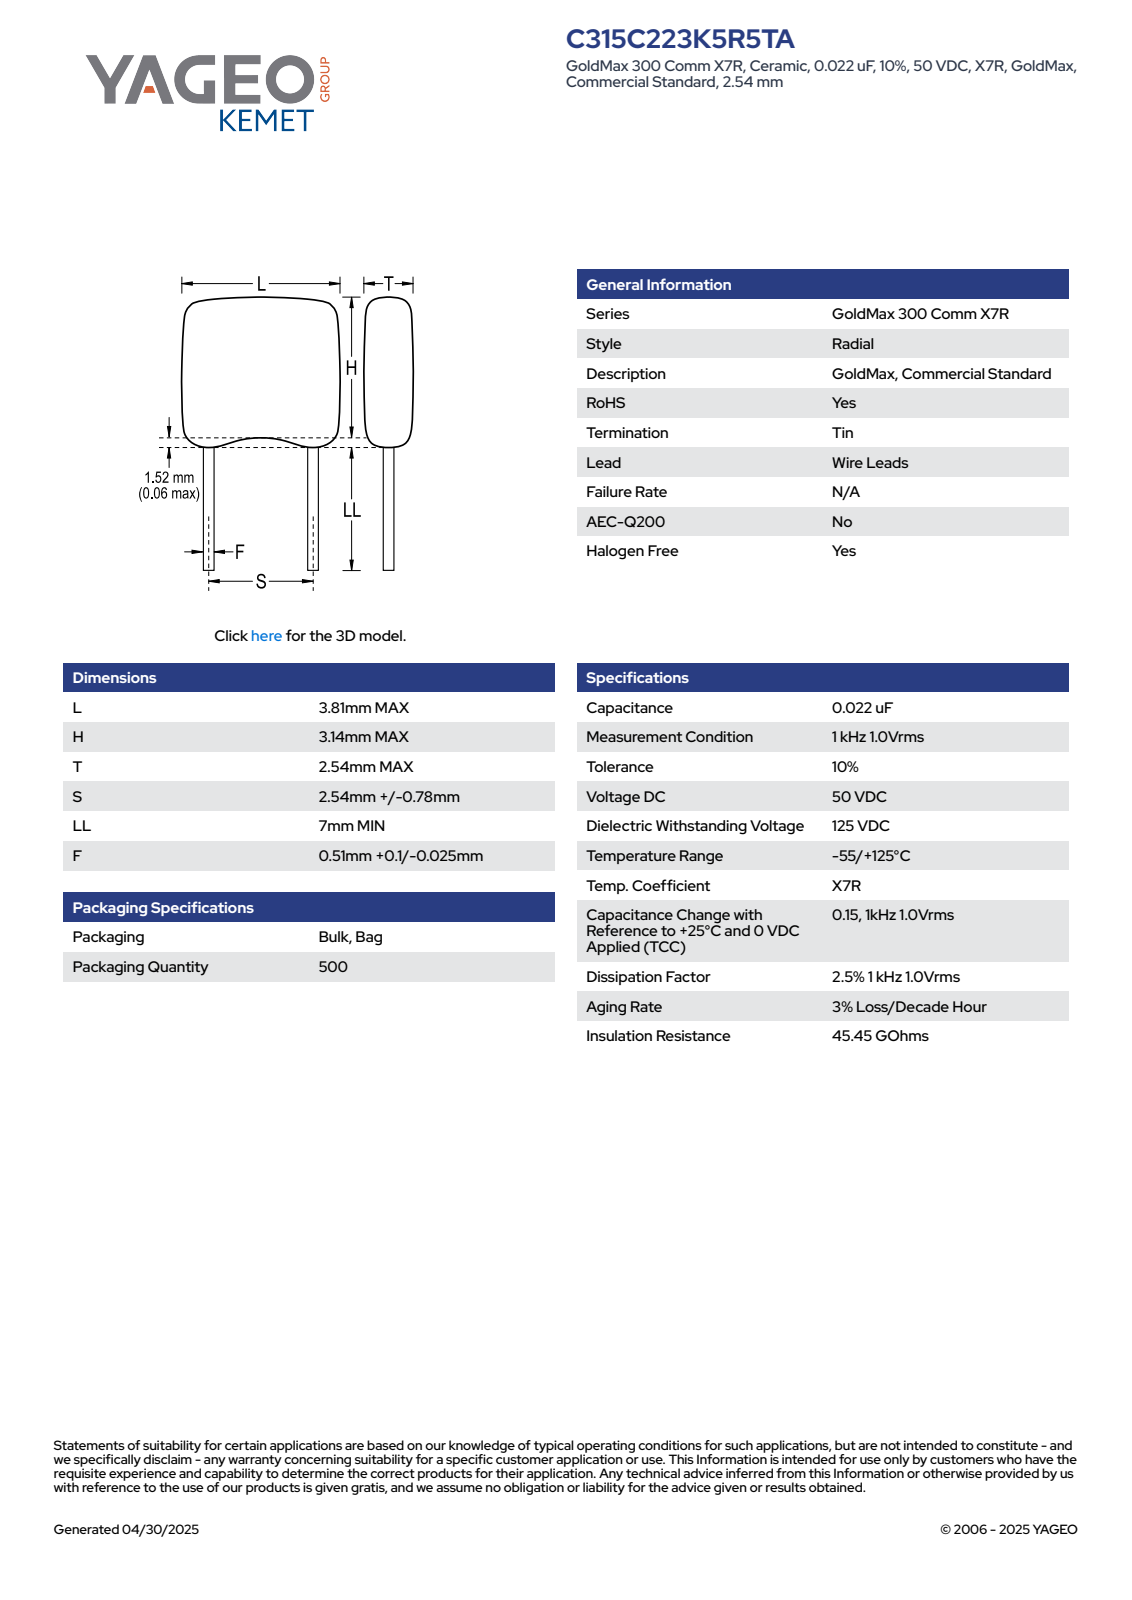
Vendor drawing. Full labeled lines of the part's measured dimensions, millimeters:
Part name (STEP PRODUCT): CCR_KRCST_C315_L3.81H3.14T2.54S2.54LL7F0.61
STEP written by: SolidWorks 2014 (AUTOMOTIVE_DESIGN)
Units: millimetres
Bodies: 4 solids, 83 faces (65 planar, 14 cylindrical, 4 other)
Overall size (bounding box): 11.66 × 3.81 × 2.54
Volume: 45 mm³ · Surface area: 93 mm²
Round bosses / shafts (diameter × count): ⌀0.61 ×2
Partial cylindrical surfaces — rounded edges, fillets, slot ends (radius × count): R0.75 ×10
Main face-to-face distances: 2.54, 3.81, 4.66, 7, 11.66, 0.41, 9.59, 2.59, 2.07, 9.18
